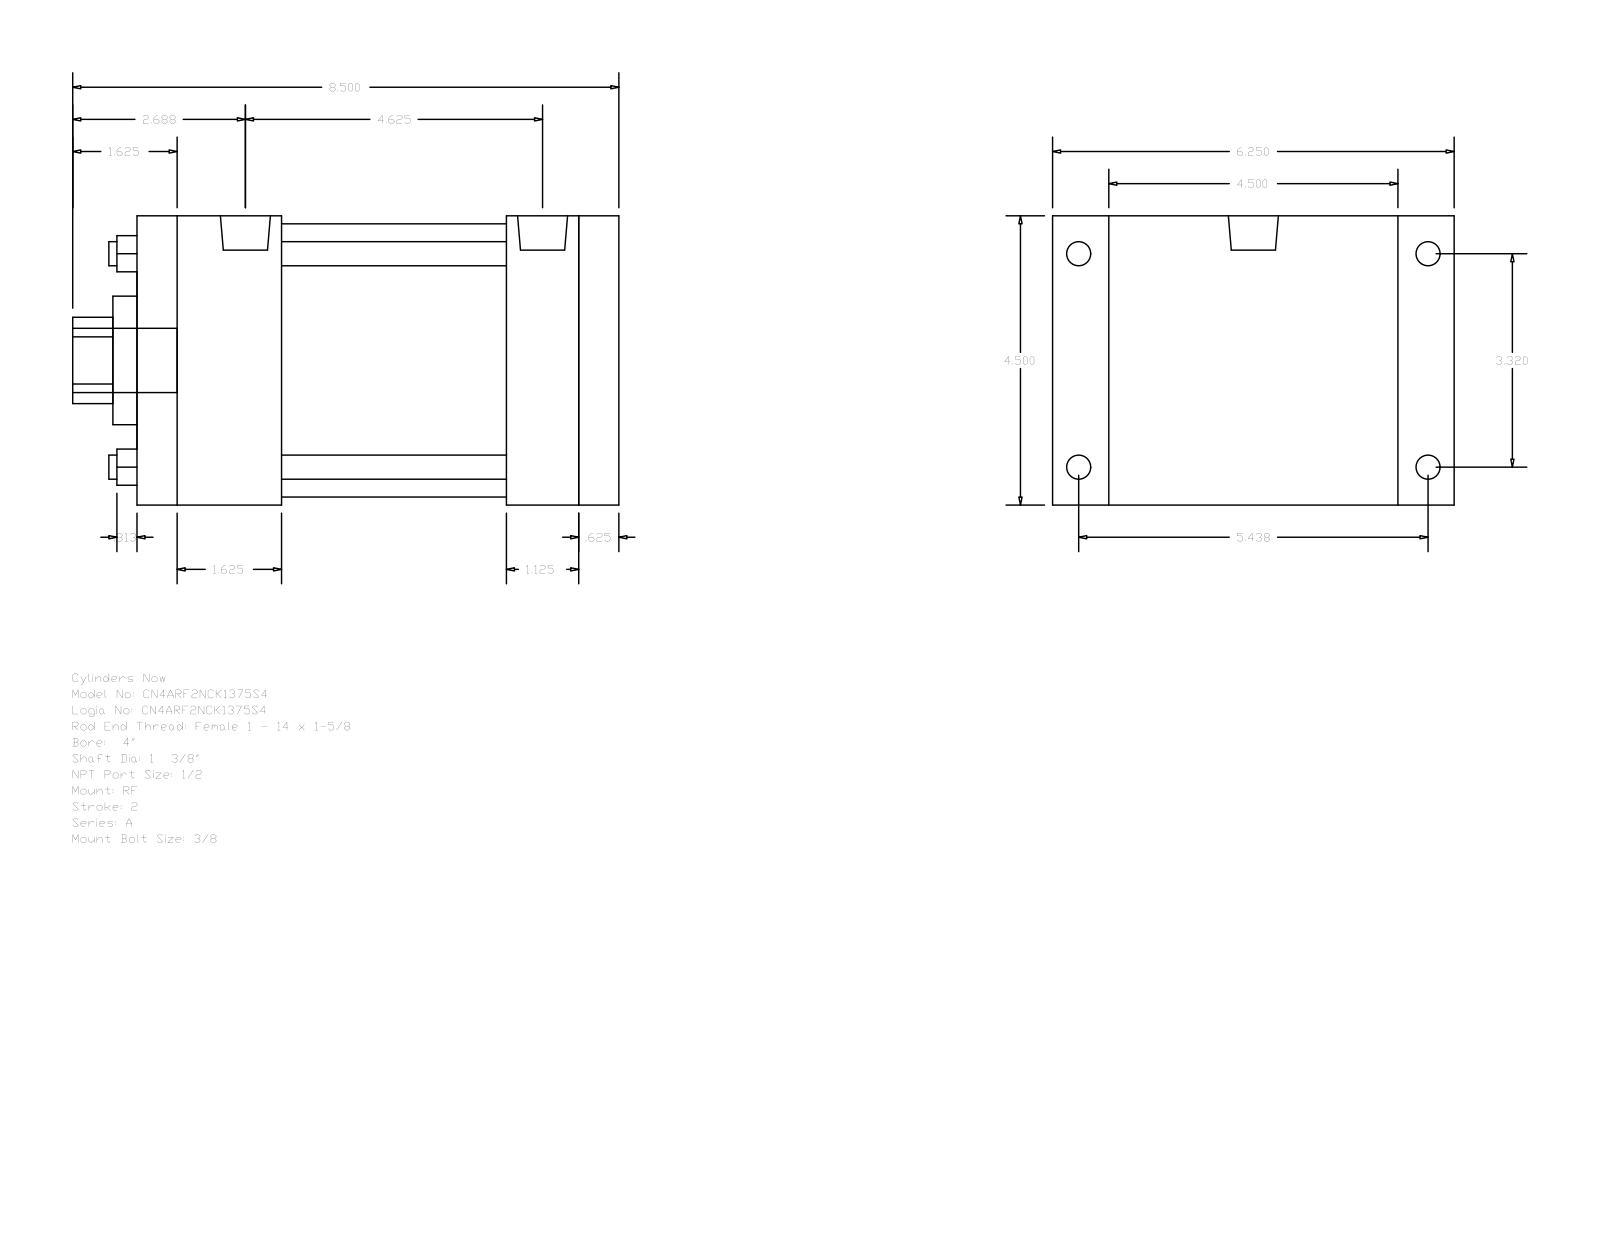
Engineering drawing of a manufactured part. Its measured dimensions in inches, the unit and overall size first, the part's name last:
Units: inches
Overall size (bounding box): 8.5 × 6.25 × 4.5
Round holes (diameter × count): ⌀0.375 ×4, ⌀1.375 ×1, ⌀2 ×1, ⌀4.25 ×1
Round bosses / shafts (diameter × count): ⌀0.375 ×4, ⌀0.344 ×4, ⌀0.778 ×2, ⌀1 ×1
Partial cylindrical surfaces — rounded edges, fillets, slot ends (radius × count): R0.672 ×1
Main face-to-face distances: 4.5, 7.5, 0.625, 6.875, 1.125, 0.875, 5.375, 5.75, 1.75, 2.25
Hole centre spacings: 2.347, 3.32, 4.695
Bodies: 0 solids, 92 faces (64 planar, 28 cylindrical, 0 other)
Part name (STEP PRODUCT): A_RF__0400_1.375
STEP written by: GSSL Pune (CONFIG_CONTROL_DESIGN)
